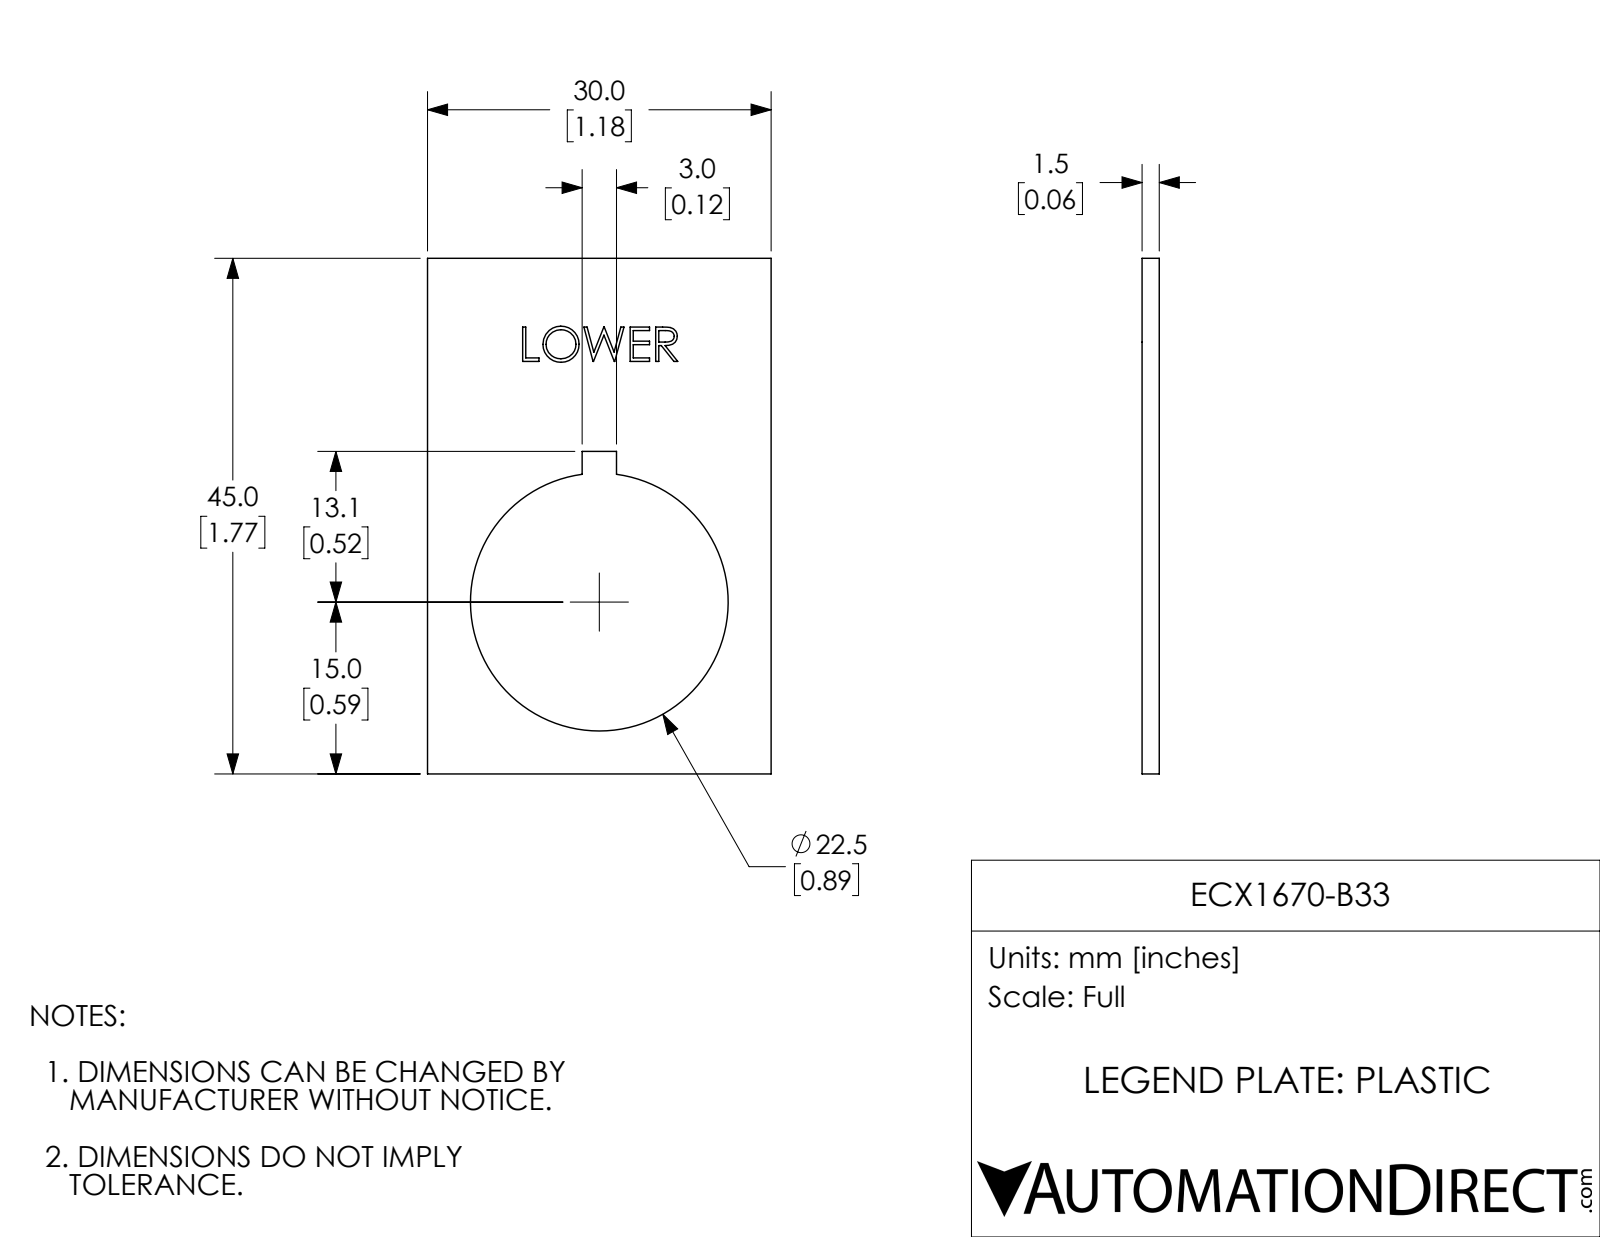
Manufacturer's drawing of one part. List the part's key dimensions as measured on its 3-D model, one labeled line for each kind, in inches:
Part name (STEP PRODUCT): ECX1670-B33
STEP written by: SolidWorks 2017 (AUTOMOTIVE_DESIGN)
Units: inches
Bodies: 1 solid, 74 faces (58 planar, 3 cylindrical, 13 other)
Overall size (bounding box): 1.772 × 1.181 × 0.059
Volume: 0.087 in³ · Surface area: 3.46 in²
Round holes (diameter × count): ⌀0.886 ×1
Main face-to-face distances: 0.059, 1.181, 1.772, 0.058, 0.531, 0.65, 1.108, 0.663, 0.118, 0.012
